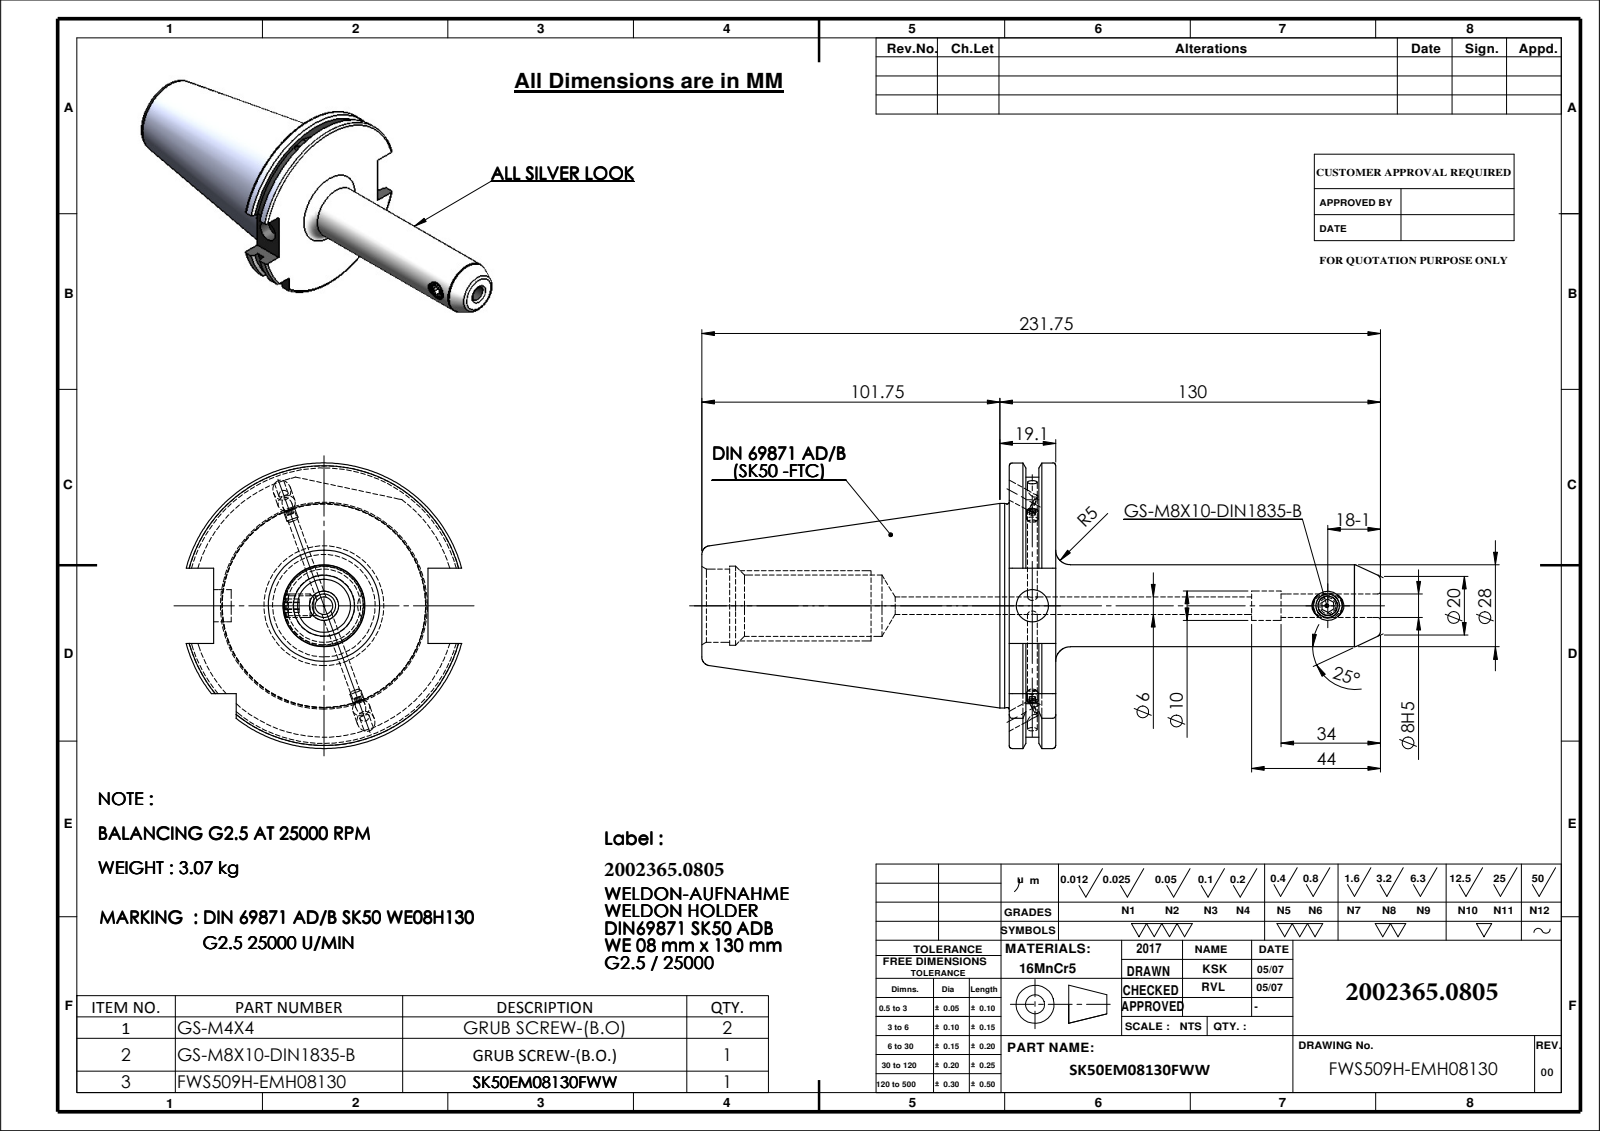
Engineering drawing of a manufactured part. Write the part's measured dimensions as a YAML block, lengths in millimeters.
part_name: "SK50EM08130FWW; 91506-WE708130; M8X10._DIN 913 - M8 x 8-N; Copy of M4X4_DIN 913 - M4 x 4-N"
step_written_by: "SolidWorks 2009 (CONFIG_CONTROL_DESIGN)"
units: millimeters
bodies: {solids: 4, faces: 168, planar: 53, cylindrical: 55, other: 60}
overall_size: [231.75, 97.5, 94.05]
volume: 398884
surface_area: 55190
round_holes:
  - {diameter: 6, count: 3}
  - {diameter: 10, count: 2}
  - {diameter: 3.3, count: 1}
  - {diameter: 6.8, count: 1}
  - {diameter: 8, count: 1}
  - {diameter: 11, count: 1}
  - {diameter: 21, count: 1}
  - {diameter: 25, count: 1}
  - {diameter: 27, count: 1}
round_bosses_or_shafts:
  - {diameter: 4, count: 2}
  - {diameter: 69.85, count: 1}
  - {diameter: 69.45, count: 1}
  - {diameter: 28, count: 1}
  - {diameter: 8, count: 1}
partial_cylinders:
  - {radius: 44.9, count: 1}
  - {radius: 48.75, count: 1}
face_to_face_distances: [15.9, 10.15, 5.75, 5.66, 4.49, 10.24, 104.95, 110.61, 115.1, 120.85]
hole_center_spacings: [100.9]
